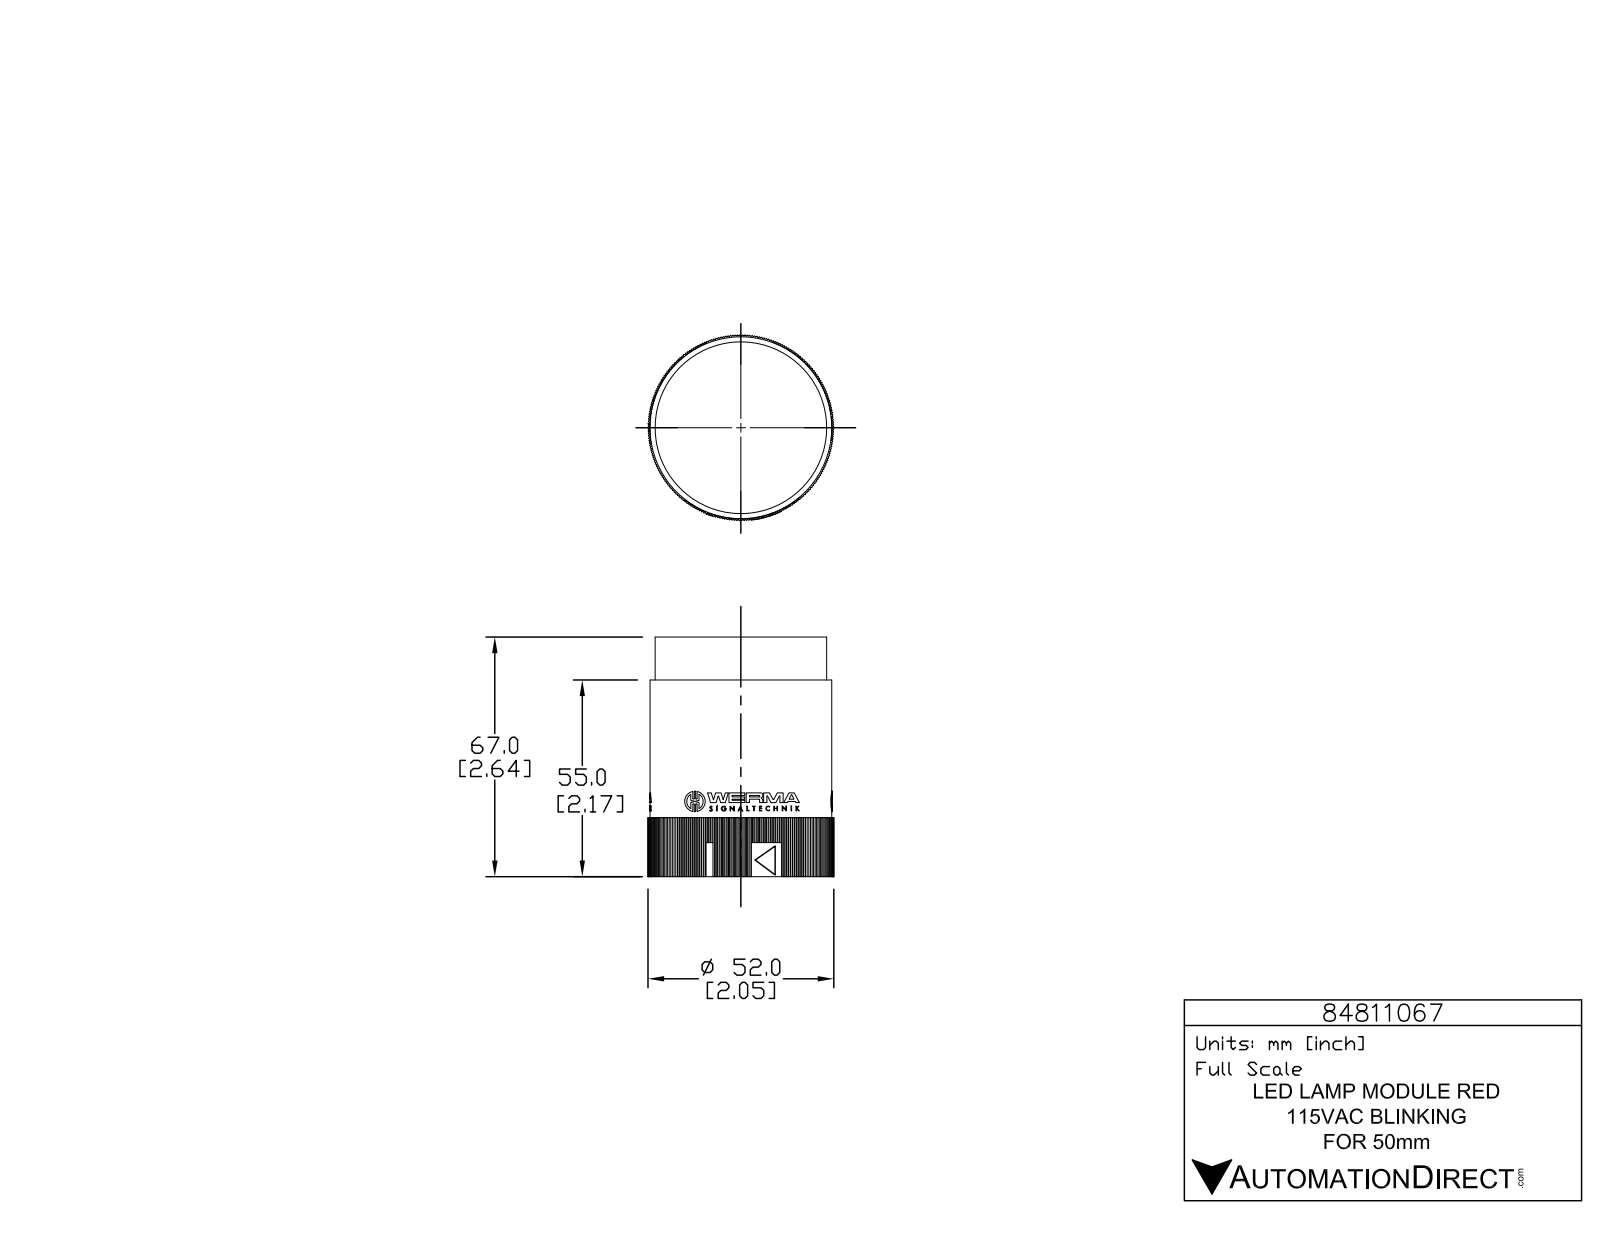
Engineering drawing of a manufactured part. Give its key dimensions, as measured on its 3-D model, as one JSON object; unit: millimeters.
{"part_name": "84811067", "step_written_by": "SolidWorks 2015 (AUTOMOTIVE_DESIGN)", "units": "millimeters", "bodies": {"solids": 1, "faces": 1265, "planar": 1020, "cylindrical": 245, "other": 0}, "overall_size": [67, 52, 52], "volume_mm3": 112600, "surface_area_mm2": 17820, "round_holes": [[1, 3], [48.2, 1]], "round_bosses_or_shafts": [[5.7, 3], [1.4, 3], [50.9, 1], [48, 1]], "partial_cylinders_radius": [[0.2, 6], [0.2, 6], [0.2, 6], [3.3, 6], [0.1, 3], [0.1, 3], [0.2, 3], [0.2, 3]], "face_to_face_distances": [55, 36.3, 36.3, 36.3, 12, 67, 36.3, 36.3, 43, 50.5]}
